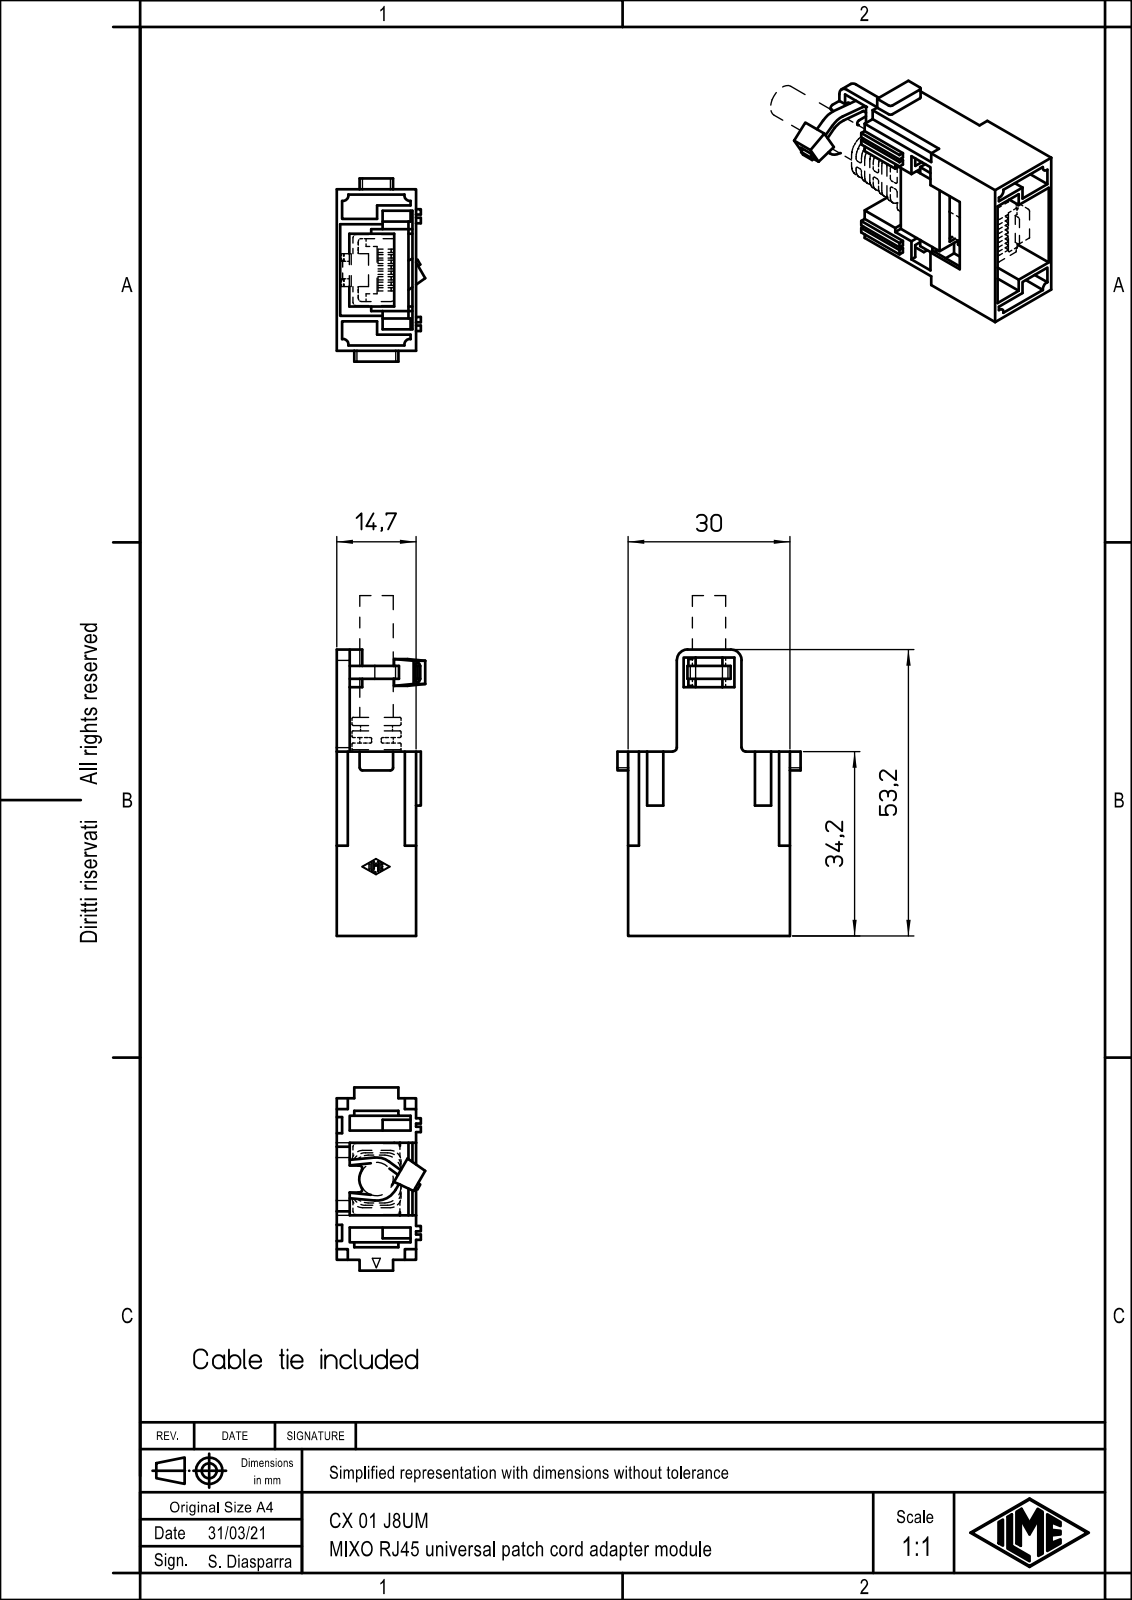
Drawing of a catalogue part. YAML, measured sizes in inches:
part_name: "CX_01_J8UM"
step_written_by: "Creo Elements/Direct Modeling 20.1B 02-Apr-2019 (C) Parametric Technology GmbH (AUTOMOTIVE_DESIGN)"
units: inches
bodies: {solids: 1, faces: 219, planar: 191, cylindrical: 28, other: 0}
overall_size: [2.093, 1.339, 0.646]
volume: 0.365
surface_area: 13.71
partial_cylinders:
  - {radius: 0.02, count: 10}
  - {radius: 0.039, count: 4}
  - {radius: 0.03, count: 2}
  - {radius: 0.059, count: 2}
  - {radius: 0.079, count: 2}
  - {radius: 0.118, count: 2}
  - {radius: 0.157, count: 2}
  - {radius: 0.126, count: 1}
face_to_face_distances: [0.039, 0.089, 0.026, 0.118, 0.484, 0.925, 0.197, 0.069, 0.094, 0.553]
